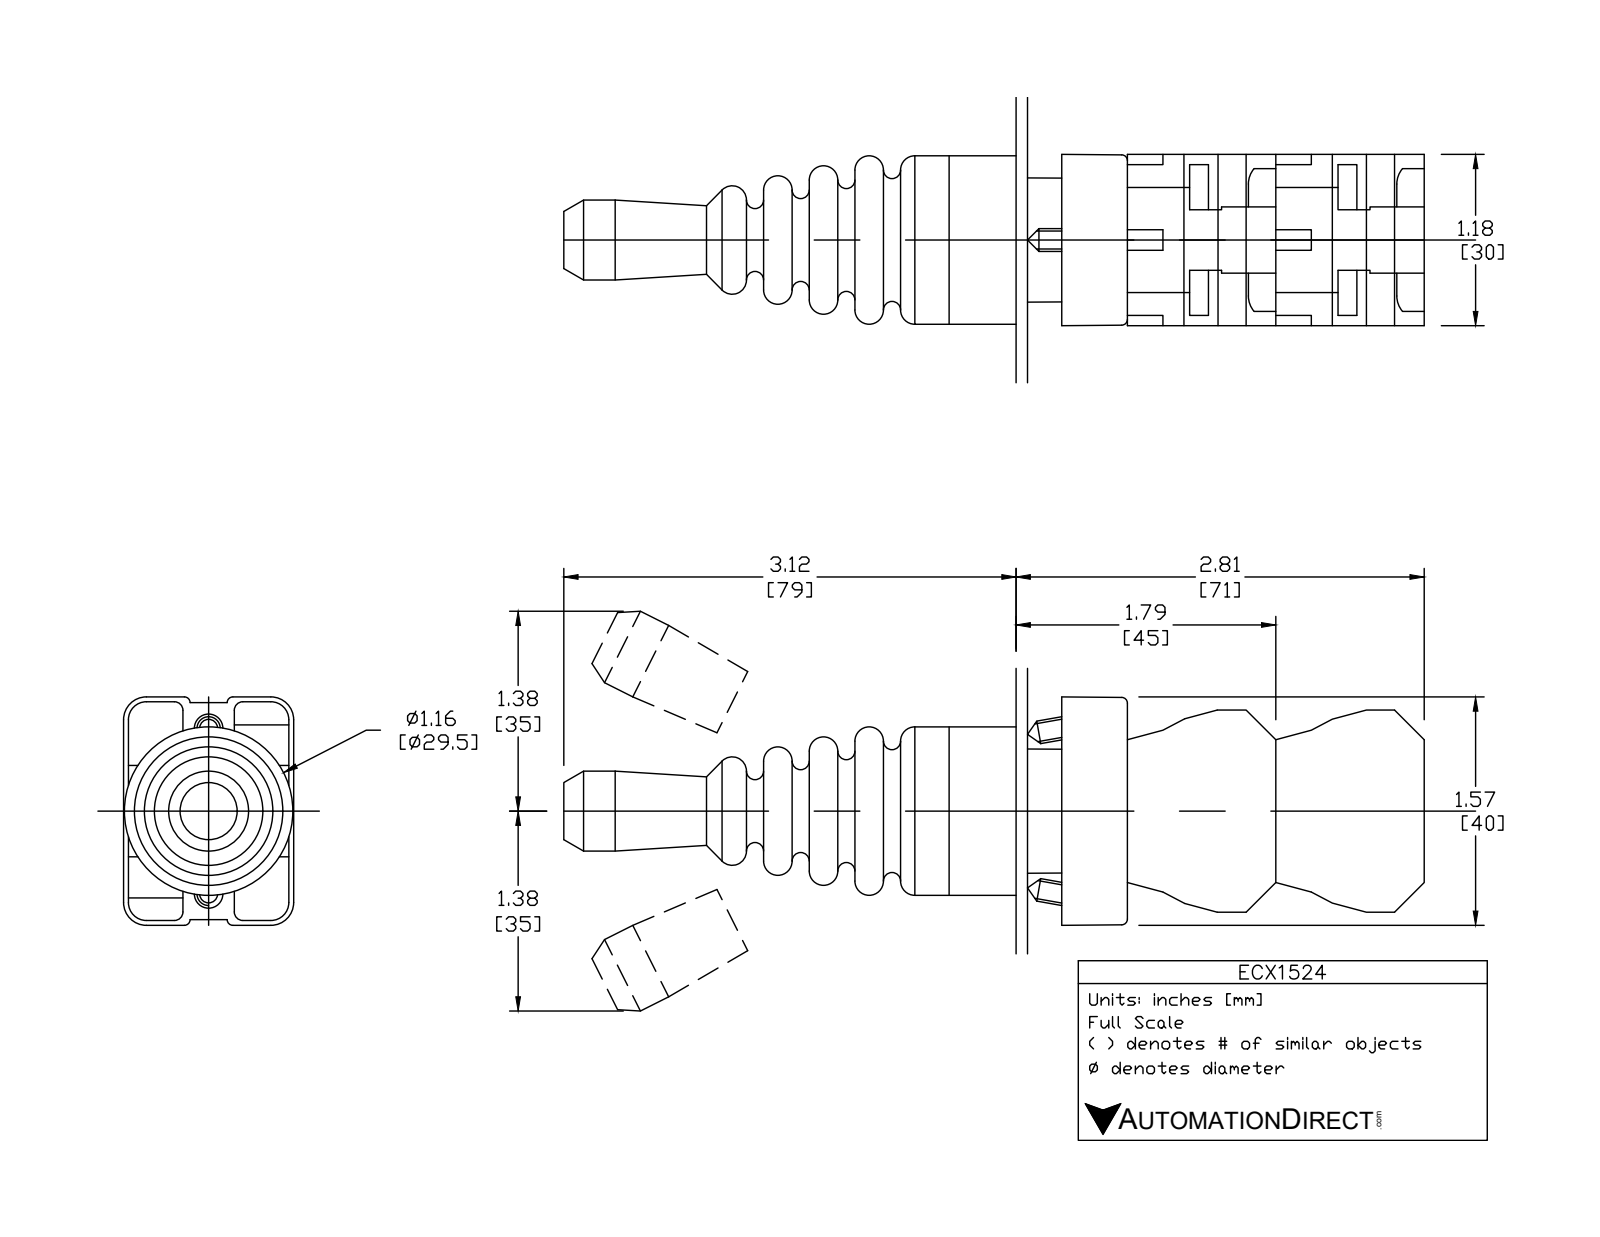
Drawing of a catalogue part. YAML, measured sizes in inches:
part_name: "ECX1524"
step_written_by: "SolidWorks 2017 (AUTOMOTIVE_DESIGN)"
units: inches
bodies: {solids: 9, faces: 707, planar: 450, cylindrical: 172, other: 85}
overall_size: [5.909, 1.581, 1.181]
volume: 4.87
surface_area: 51.32
round_holes:
  - {diameter: 0.079, count: 4}
  - {diameter: 0.087, count: 2}
  - {diameter: 0.124, count: 2}
  - {diameter: 0.13, count: 2}
  - {diameter: 0.197, count: 1}
  - {diameter: 0.878, count: 1}
  - {diameter: 0.888, count: 1}
round_bosses_or_shafts:
  - {diameter: 0.157, count: 2}
  - {diameter: 1.181, count: 1}
  - {diameter: 1.175, count: 1}
  - {diameter: 0.945, count: 1}
  - {diameter: 0.856, count: 1}
  - {diameter: 0.78, count: 1}
partial_cylinders:
  - {radius: 0.059, count: 24}
  - {radius: 0.041, count: 12}
  - {radius: 0.124, count: 12}
  - {radius: 0.157, count: 12}
  - {radius: 0.039, count: 4}
  - {radius: 0.02, count: 2}
  - {radius: 0.063, count: 2}
  - {radius: 0.079, count: 2}
face_to_face_distances: [0.591, 0.579, 1.024, 1.169, 1.193, 2.217, 0.033, 0.031, 0.309, 0.269]
hole_center_spacings: [0.236, 0.636, 0.591, 0.257, 0.472, 0.544, 0.756, 0.1]
